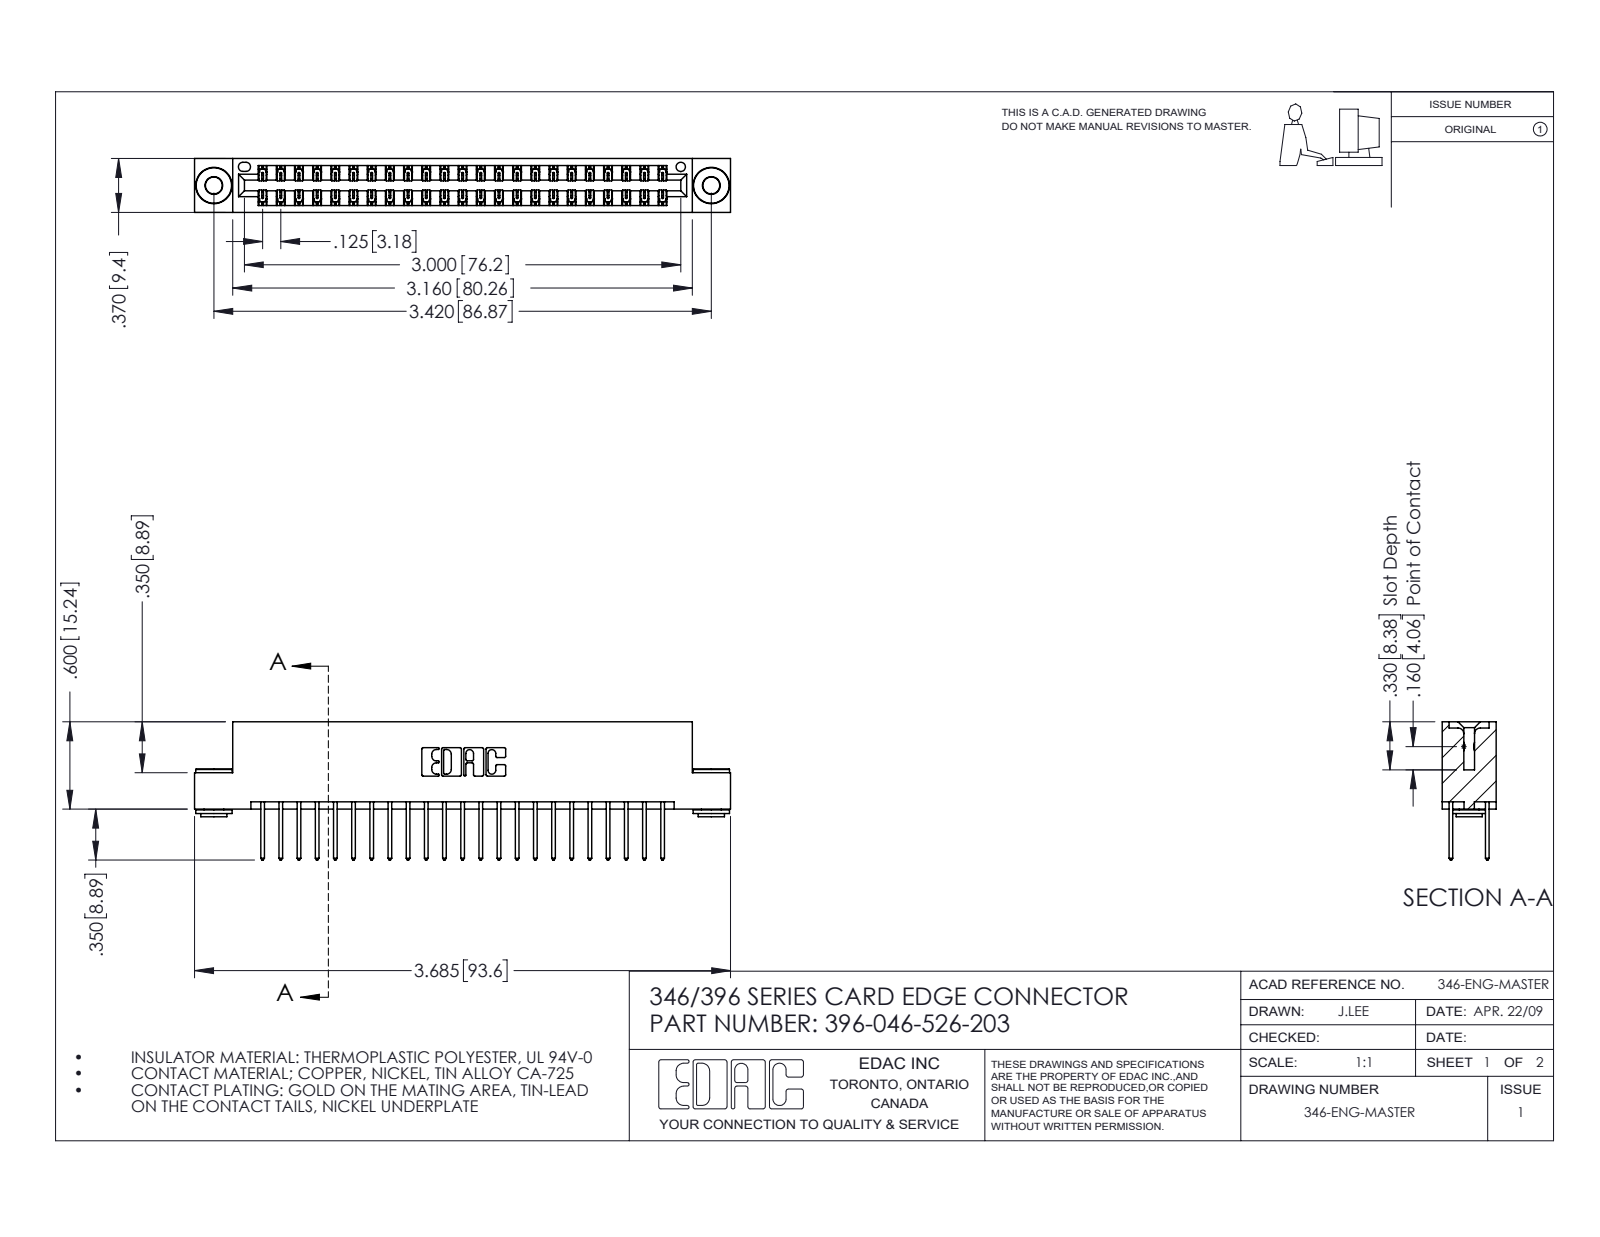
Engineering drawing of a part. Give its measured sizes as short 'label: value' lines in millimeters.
name: 396-046-526-203; 346 Part_Flush Mounting Lugs - 0.156 Dia-TH; 345-292-001_345-293-126; 345-250-002_345-250-002-102
written by: SolidWorks 2016 (CONFIG_CONTROL_DESIGN)
unit: mm
bodies: 49 solids, 2552 faces (1696 planar, 848 cylindrical, 8 other)
size: 93.6 × 24.1 × 9.4
volume: 9 080 mm³; area: 12 730 mm²
holes: 2× ⌀2.9, 2× ⌀4, 1× ⌀1.6
bosses: 2× ⌀6.4, 2× ⌀4.6, 2× ⌀3.5
rounds: 69× R0.2, 46× R0.3, 22× R0.3, 6× R0.2, 6× R0.8, 3× R0.7, 2× R0.4, 2× R0.6
face distances: 1.2, 8.2, 6.4, 9.4, 0.6, 1.8, 7.6, 7, 3.8, 5.6
hole spacings: 6.2, 81.6, 86.9
